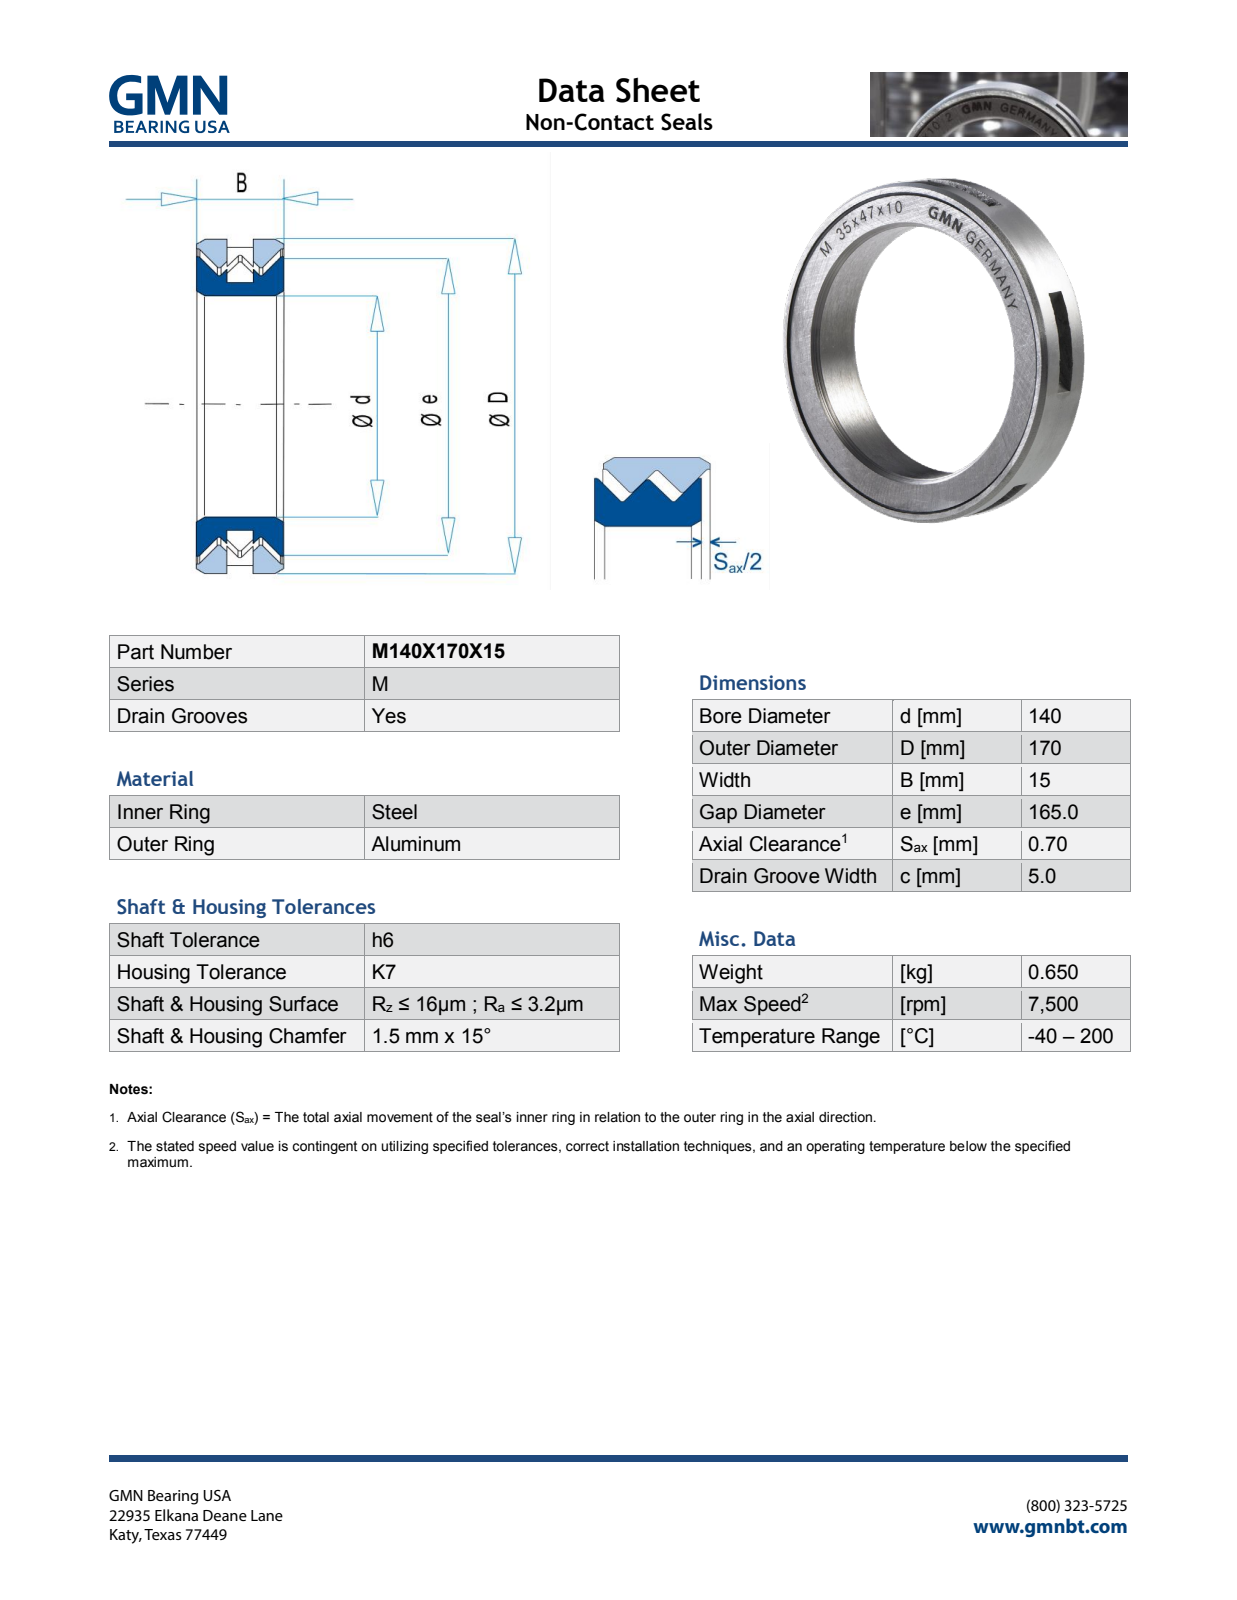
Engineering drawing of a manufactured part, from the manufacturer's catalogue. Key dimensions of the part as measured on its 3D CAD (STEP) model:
Part name (STEP PRODUCT): M140X170X15_PRT
STEP written by: PRO/ENGINEER BY PARAMETRIC TECHNOLOGY CORPORATION, 2013150 (AUTOMOTIVE_DESIGN)
Units: millimetres
Bodies: 2 solids, 632 faces (535 planar, 39 cylindrical, 58 other)
Overall size (bounding box): 170 × 170 × 15.07
Volume: 102 220 mm³ · Surface area: 45 638 mm²
Round holes (diameter × count): ⌀140 ×1, ⌀165.49 ×1
Round bosses / shafts (diameter × count): ⌀170 ×1, ⌀165 ×1
Partial cylindrical surfaces — rounded edges, fillets, slot ends (radius × count): R10 ×9
Main face-to-face distances: 15, 5, 10, 15.07, 5.07, 10.07, 1.17, 9.35, 8.18, 1.19
